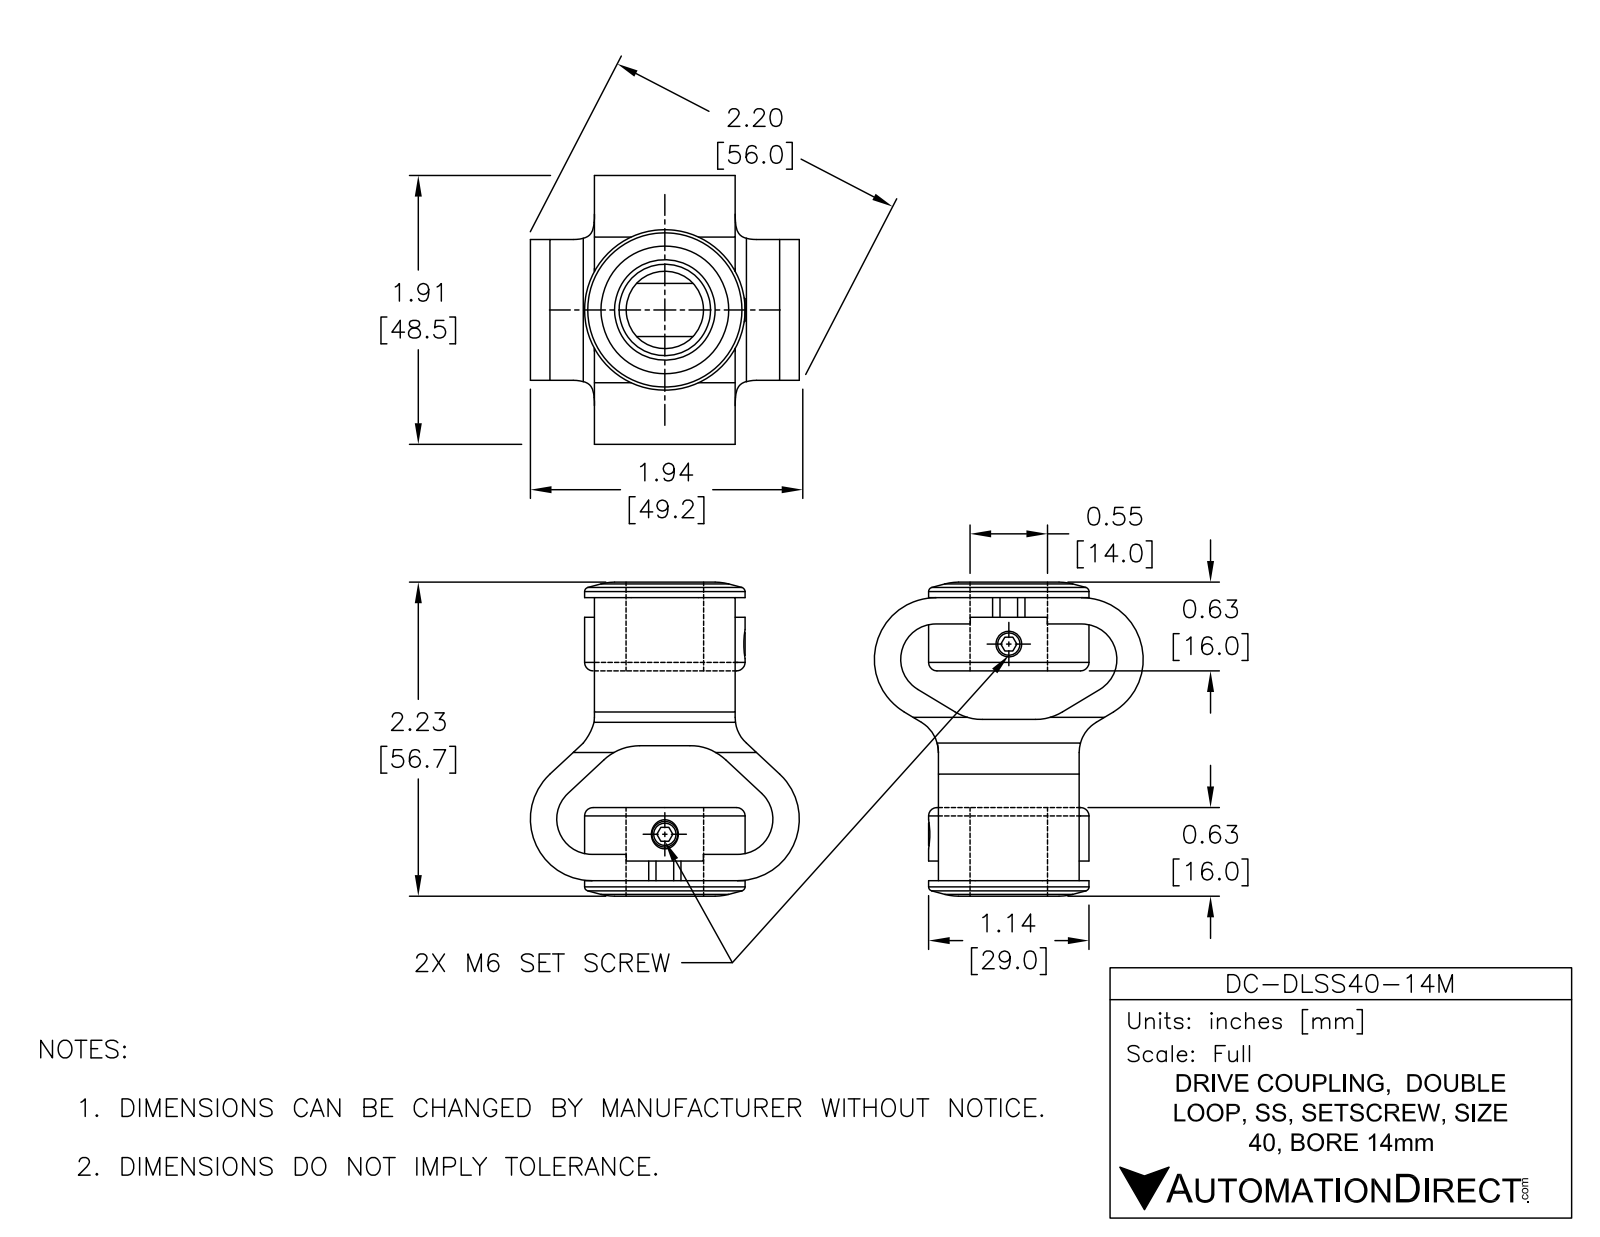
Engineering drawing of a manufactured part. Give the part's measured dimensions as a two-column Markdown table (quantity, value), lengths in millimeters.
| quantity | value |
| --- | --- |
| part name | DC-DLSS40-14M |
| STEP written by | SolidWorks 2015 (AUTOMOTIVE_DESIGN) |
| units | millimeters |
| bodies | 1 solid, 187 faces (90 planar, 49 cylindrical, 48 other) |
| overall size | 56.67 × 48.51 × 48.51 |
| volume | 33 632 mm³ |
| surface area | 15 088 mm² |
| round holes (diameter × count) | 4.14 × 2, 14 × 1 |
| round bosses / shafts (diameter × count) | 28.96 × 1 |
| partial cylindrical surfaces (radius × count) | 6.35 × 8, 6.36 × 4, 9.53 × 4, 11.11 × 3, 10.41 × 1, 11.11 × 1 |
| main face-to-face distances | 25.4, 4.75, 24.67, 15.9, 8.77, 11.15, 13.52, 21.98, 24.35, 4.76 |
